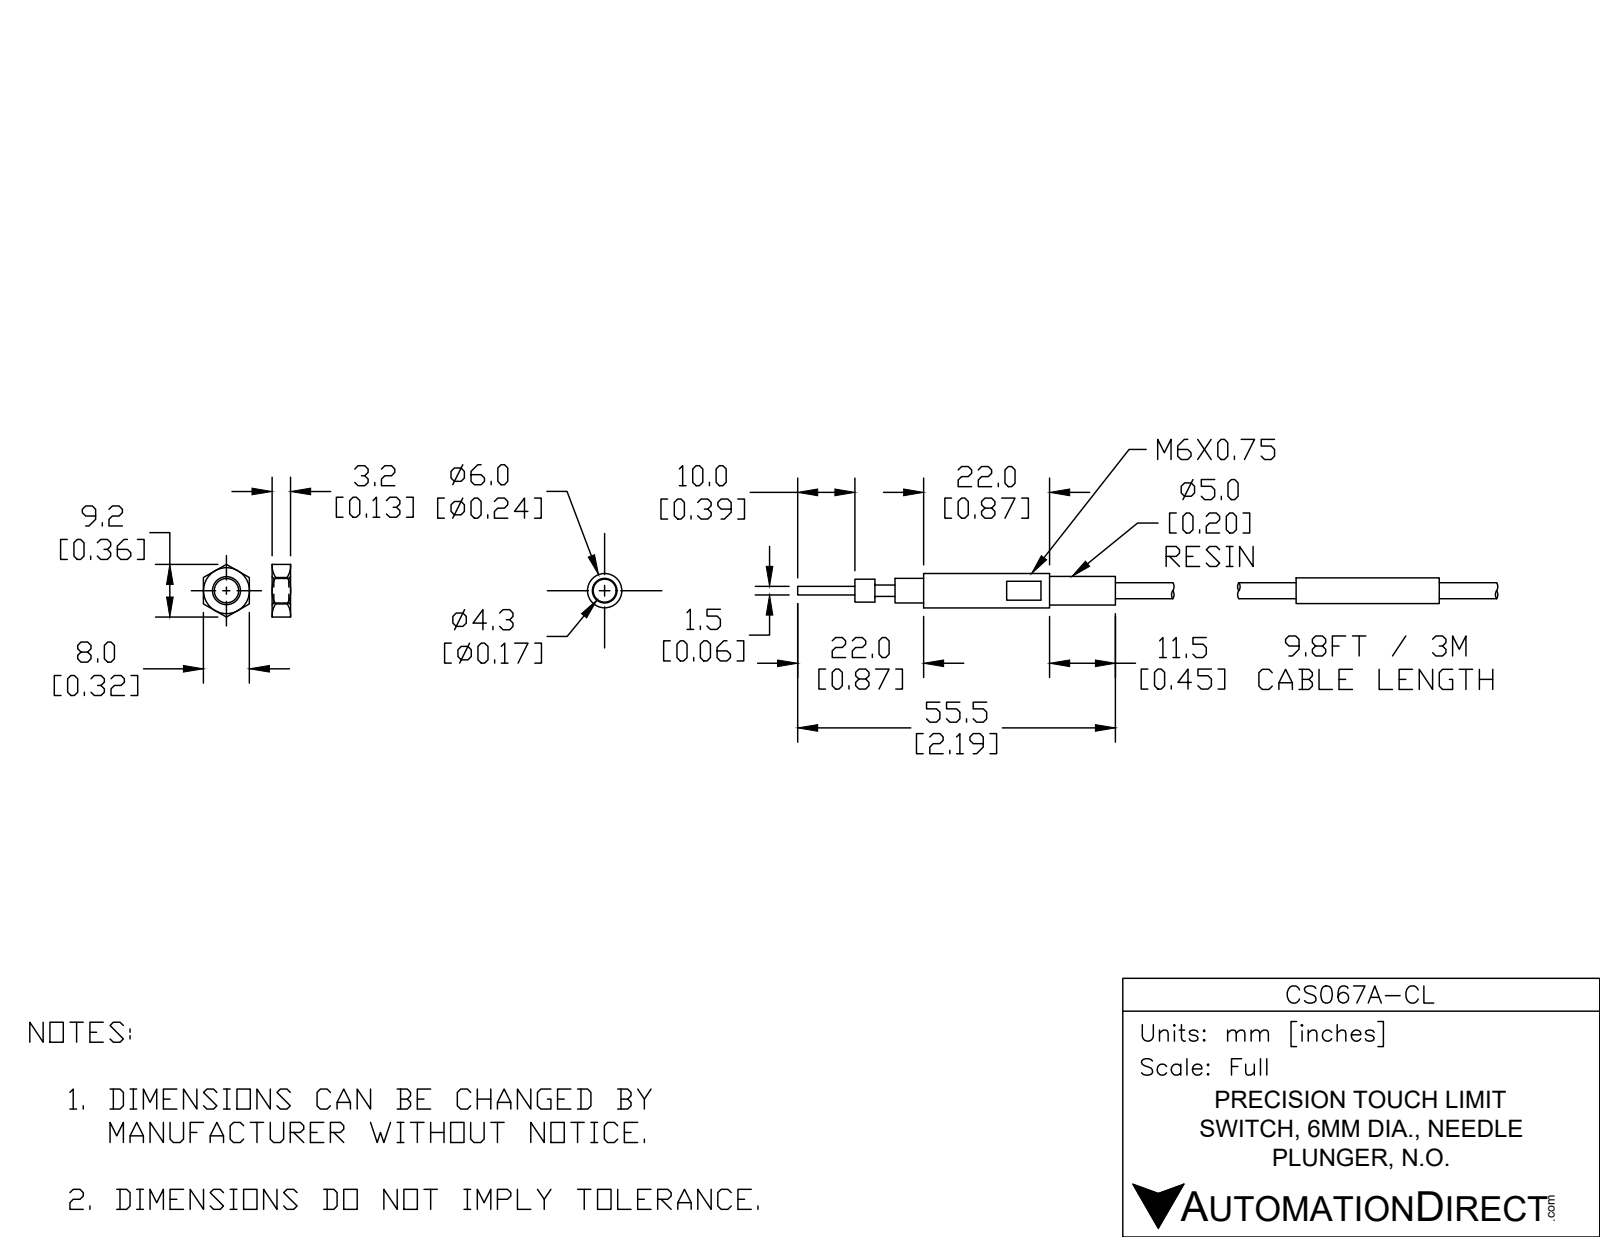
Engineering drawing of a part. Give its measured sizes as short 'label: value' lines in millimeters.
name: CS067A-CL
written by: SolidWorks 2017 (CONFIG_CONTROL_DESIGN)
unit: mm
bodies: 1 solid, 144 faces (16 planar, 78 cylindrical, 50 other)
size: 113.5 × 6 × 6
volume: 1 496 mm³; area: 1 714 mm²
bosses: 1× ⌀6, 1× ⌀5, 1× ⌀4.5, 1× ⌀4.3, 1× ⌀4, 1× ⌀2.8, 1× ⌀2, 1× ⌀1.5
face distances: 5, 3.5, 38.5, 23, 7, 45.5, 42, 68.5, 93.5, 61.5
